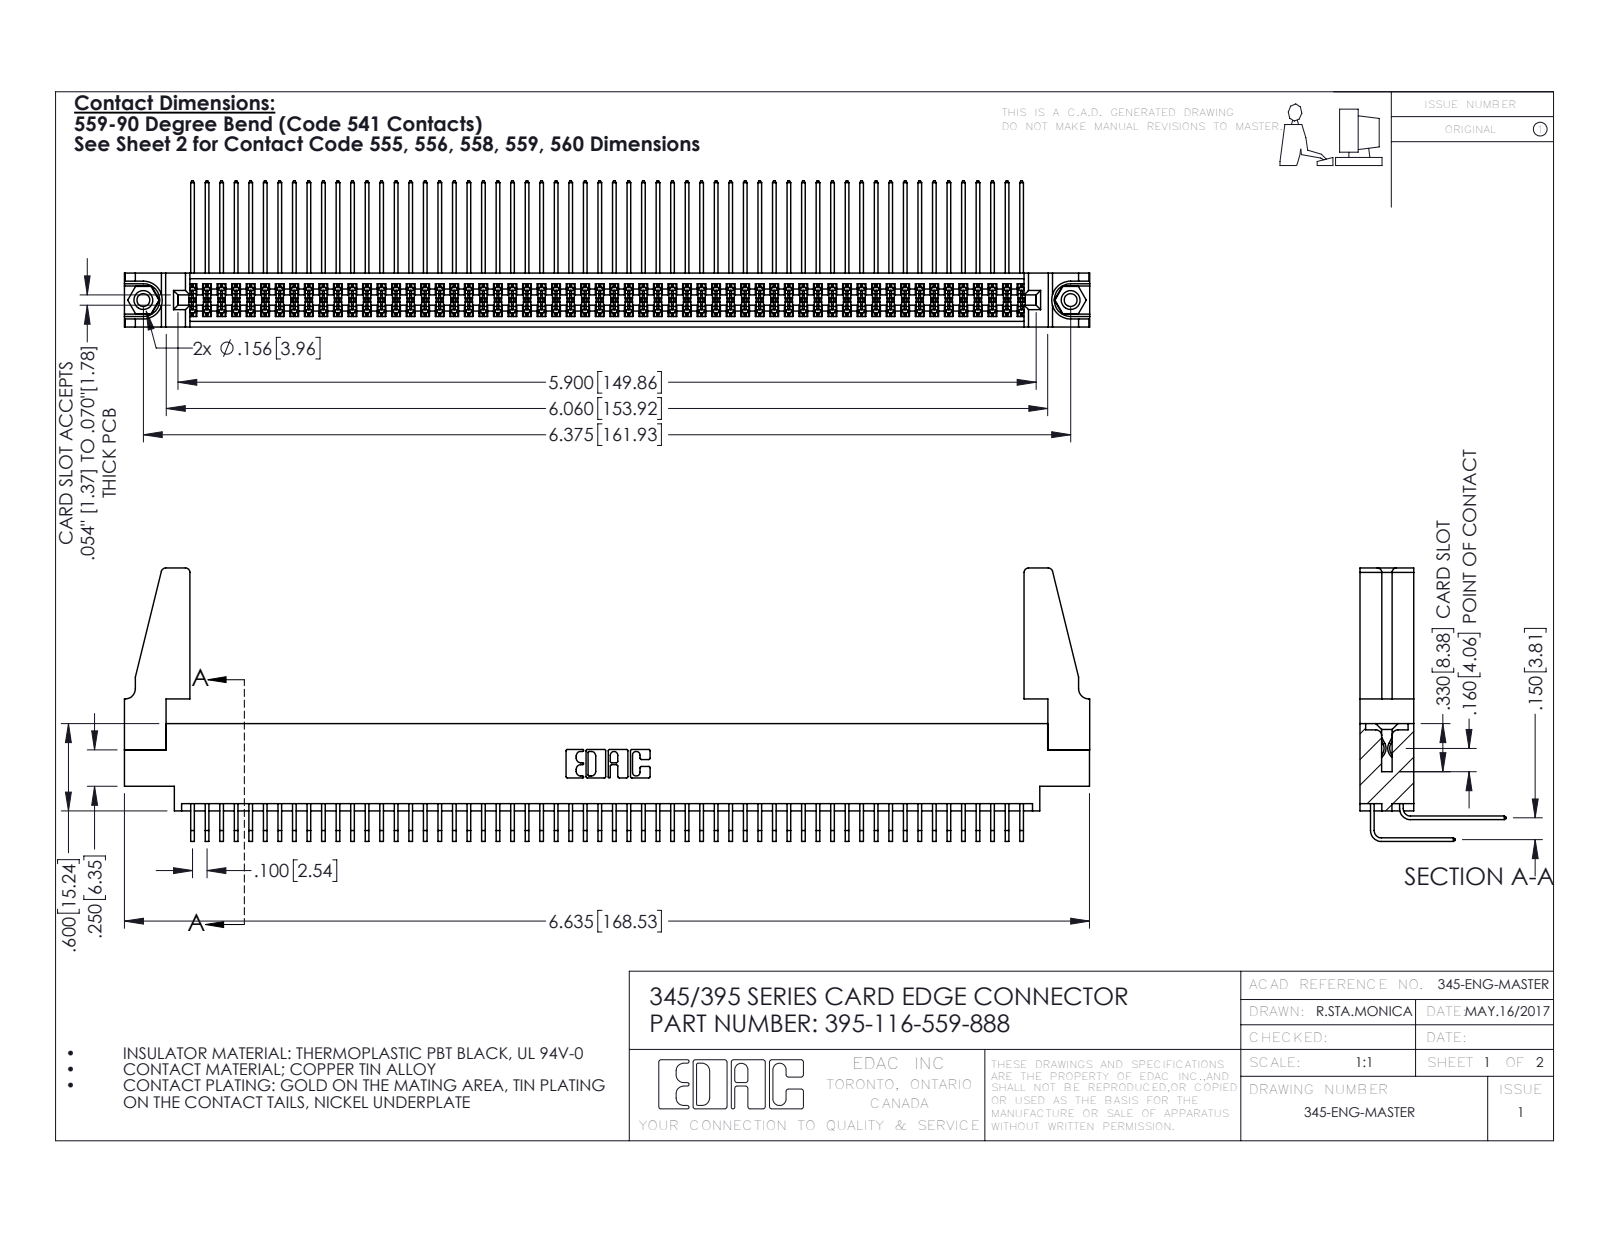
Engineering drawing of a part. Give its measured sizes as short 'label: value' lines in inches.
name: 345-292-001_558 559 Tail - 1; 345 Part_0.170 Offset - 0.156 Dia-TH; 345-220-078_345-220-088; 395-116-559-888 (+2 more)
written by: SolidWorks 2016 (CONFIG_CONTROL_DESIGN)
unit: in
bodies: 121 solids, 6286 faces (4216 planar, 2054 cylindrical, 16 other)
size: 6.636 × 1.879 × 1.005
volume: 1.241 in³; area: 49.55 in²
holes: 2× ⌀0.089, 2× ⌀0.125, 2× ⌀0.156, 1× ⌀0.064
bosses: 2× ⌀0.155
rounds: 175× R0.006, 22× R0.01, 8× R0.03, 6× R0.007, 6× R0.031, 3× R0.026, 2× R0.014, 2× R0.019
face distances: 0.072, 0.298, 0.37, 0.2, 0.098, 0.272, 0.025, 0.225, 0.15, 0.175
hole spacings: 0.27, 6.139, 6.375
